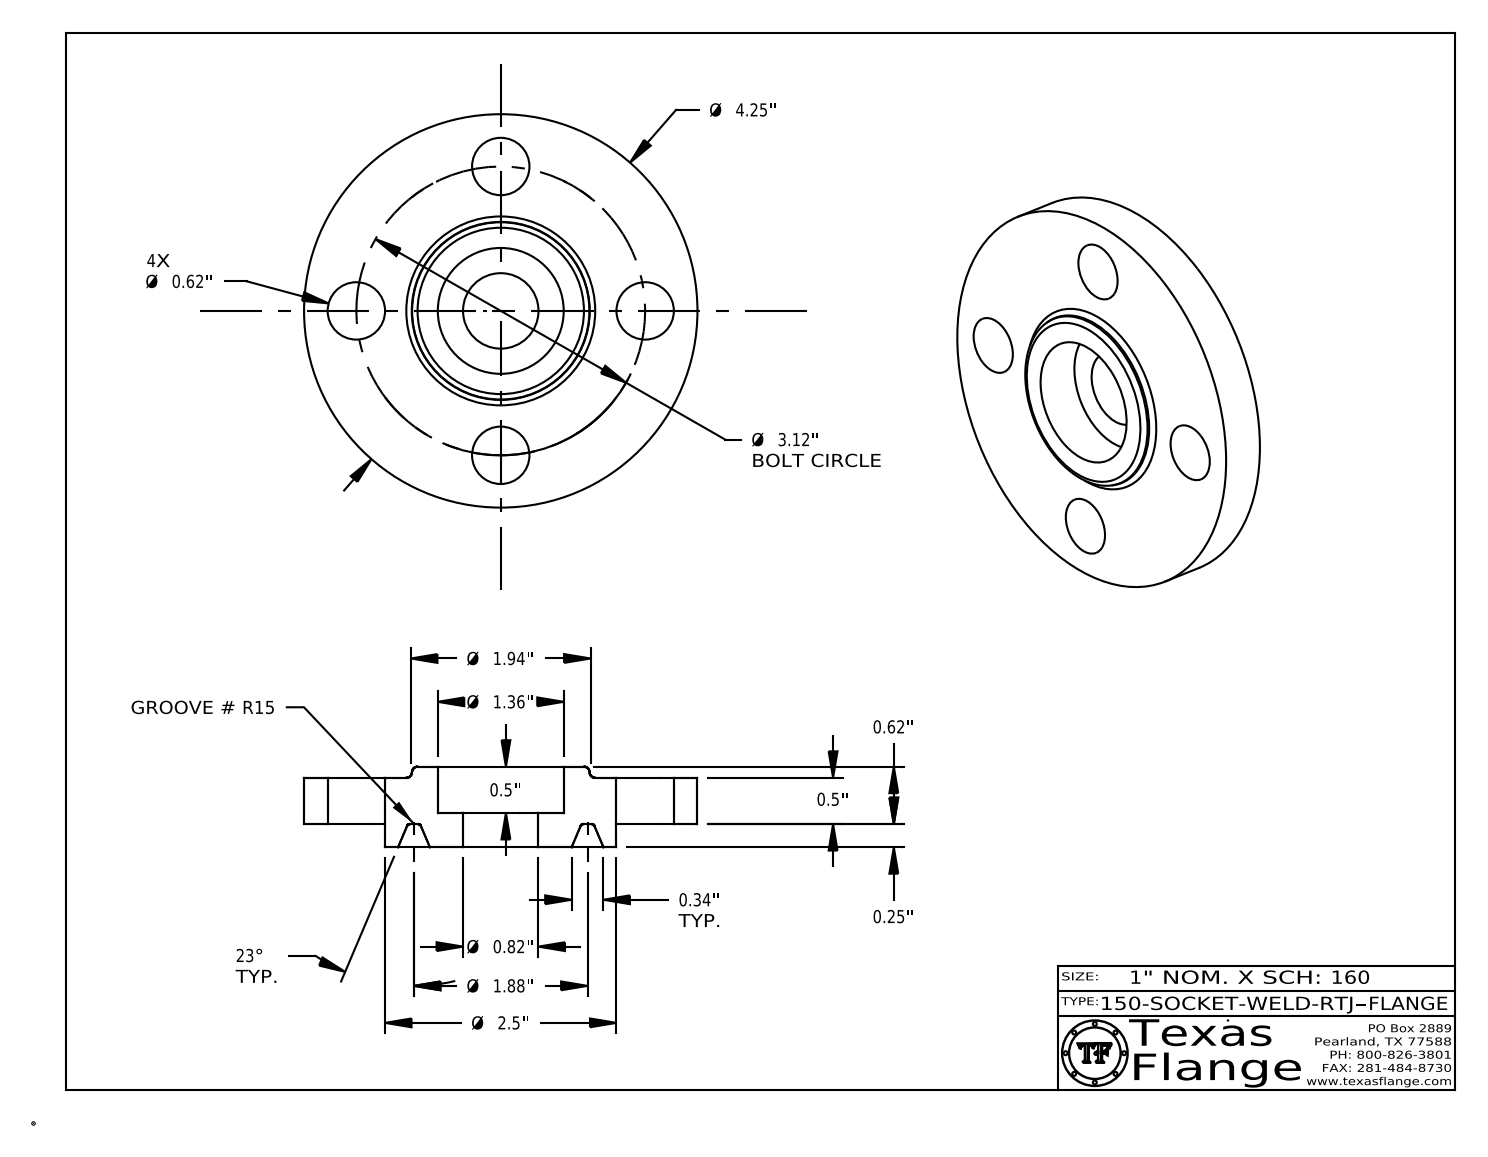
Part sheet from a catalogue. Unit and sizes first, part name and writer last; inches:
Units: inches
Overall size (bounding box): 4.25 × 4.25 × 0.87
Round holes (diameter × count): ⌀0.62 ×4, ⌀0.495 ×1, ⌀0.815 ×1, ⌀1.36 ×1
Round bosses / shafts (diameter × count): ⌀0.03 ×8, ⌀4.25 ×1, ⌀2.5 ×1, ⌀0.39 ×1
Main face-to-face distances: 0.5, 0.25, 0.75, 0.12, 0.87, 0.62, 0.37, 0.38, 0.735, 0.485
Hole centre spacings: 1.56, 2.206, 1.194, 2.882, 3.12, 1.56
Volume: 6.794 in³ · Surface area: 42.92 in²
Bodies: 1 solid, 422 faces (372 planar, 36 cylindrical, 14 other)
Part name (STEP PRODUCT): 150-SOCKET-WELD-RTJ
STEP written by: CATIA V5 STEP AP214 (AUTOMOTIVE_DESIGN)
